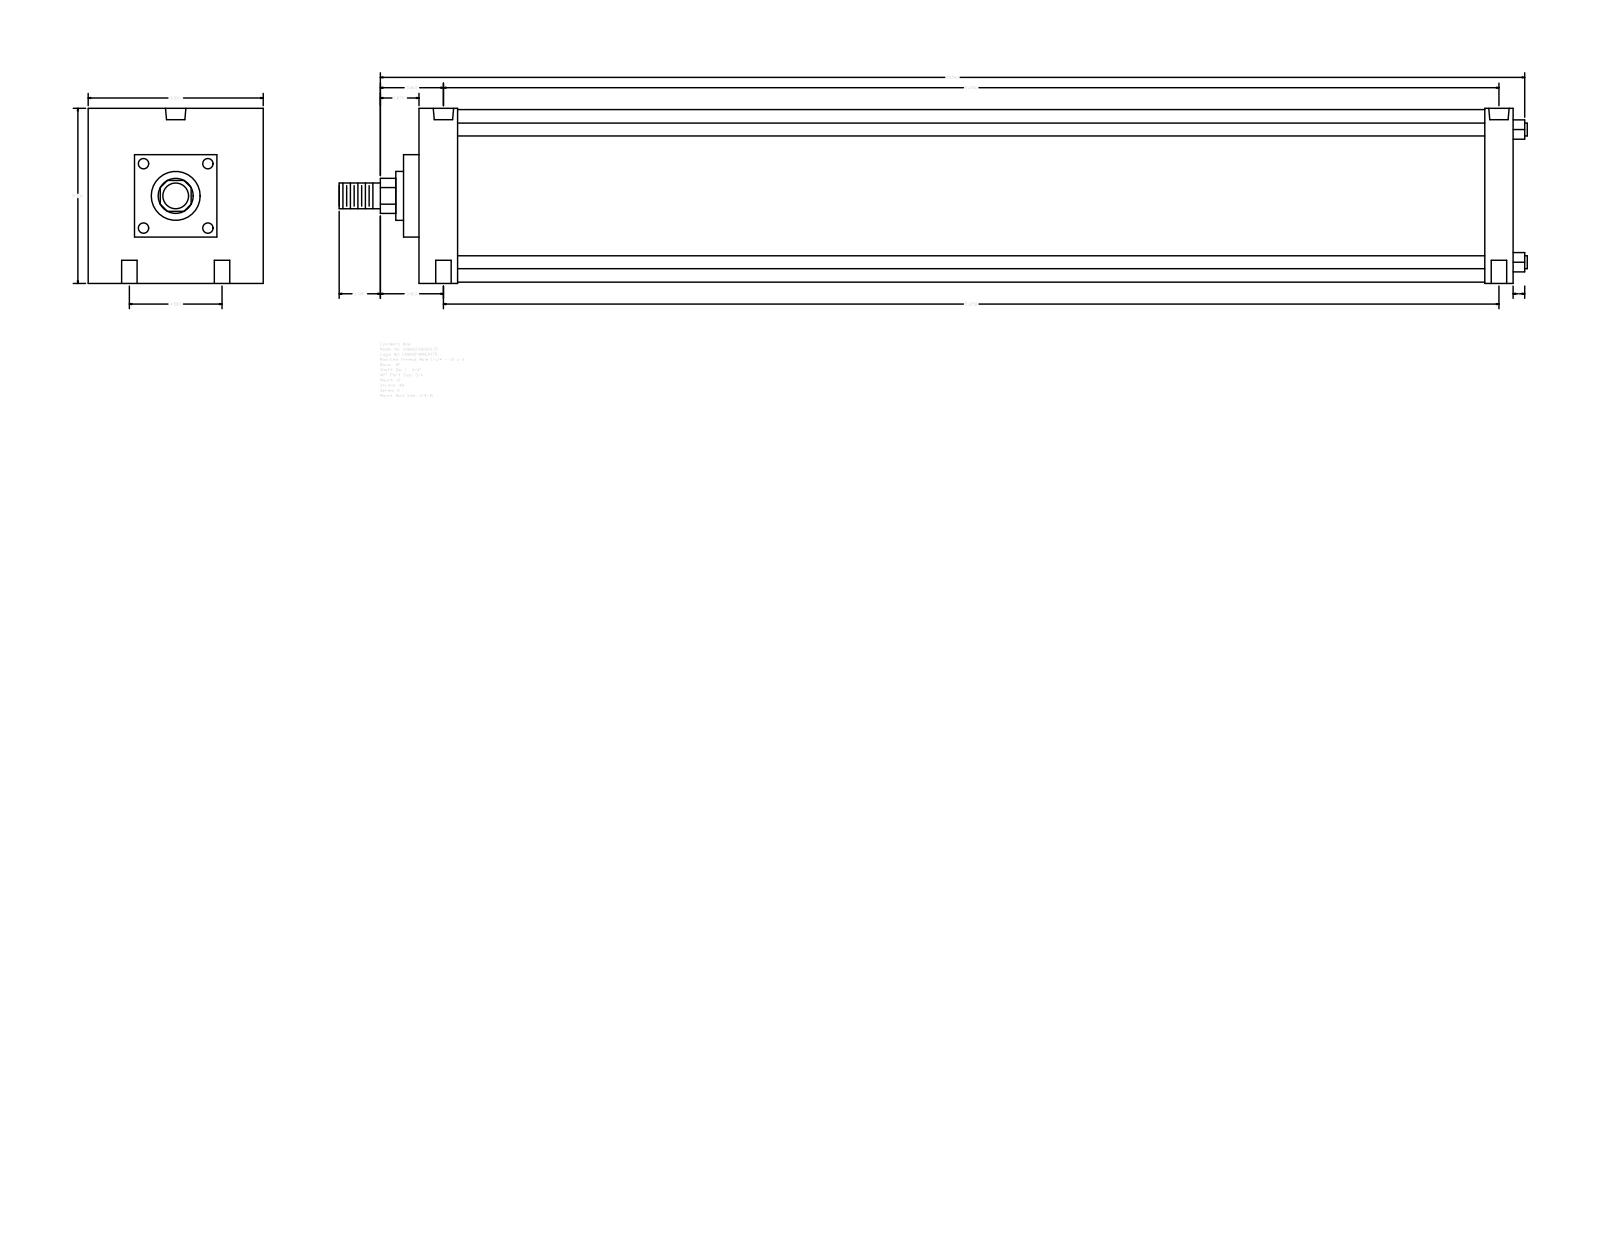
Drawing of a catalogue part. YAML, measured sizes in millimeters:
part_name: "A_SF__0800_1.75"
step_written_by: "GSSL Pune (CONFIG_CONTROL_DESIGN)"
units: millimeters
bodies: {solids: 0, faces: 93, planar: 67, cylindrical: 26, other: 0}
overall_size: [1465.26, 215.9, 215.9]
round_holes:
  - {diameter: 19.05, count: 4}
  - {diameter: 15.08, count: 2}
  - {diameter: 25.12, count: 2}
round_bosses_or_shafts:
  - {diameter: 15.88, count: 4}
  - {diameter: 212.72, count: 1}
  - {diameter: 60.33, count: 1}
  - {diameter: 44.45, count: 1}
  - {diameter: 31.75, count: 1}
partial_cylinders:
  - {radius: 21.63, count: 1}
face_to_face_distances: [1349.38, 215.9, 47.63, 1314.46, 1266.83, 1301.75, 34.92, 19.05, 158.75, 57.15]
hole_center_spacings: [57.15, 1303, 1301.75, 114.3, 1306.76, 1289.05]
